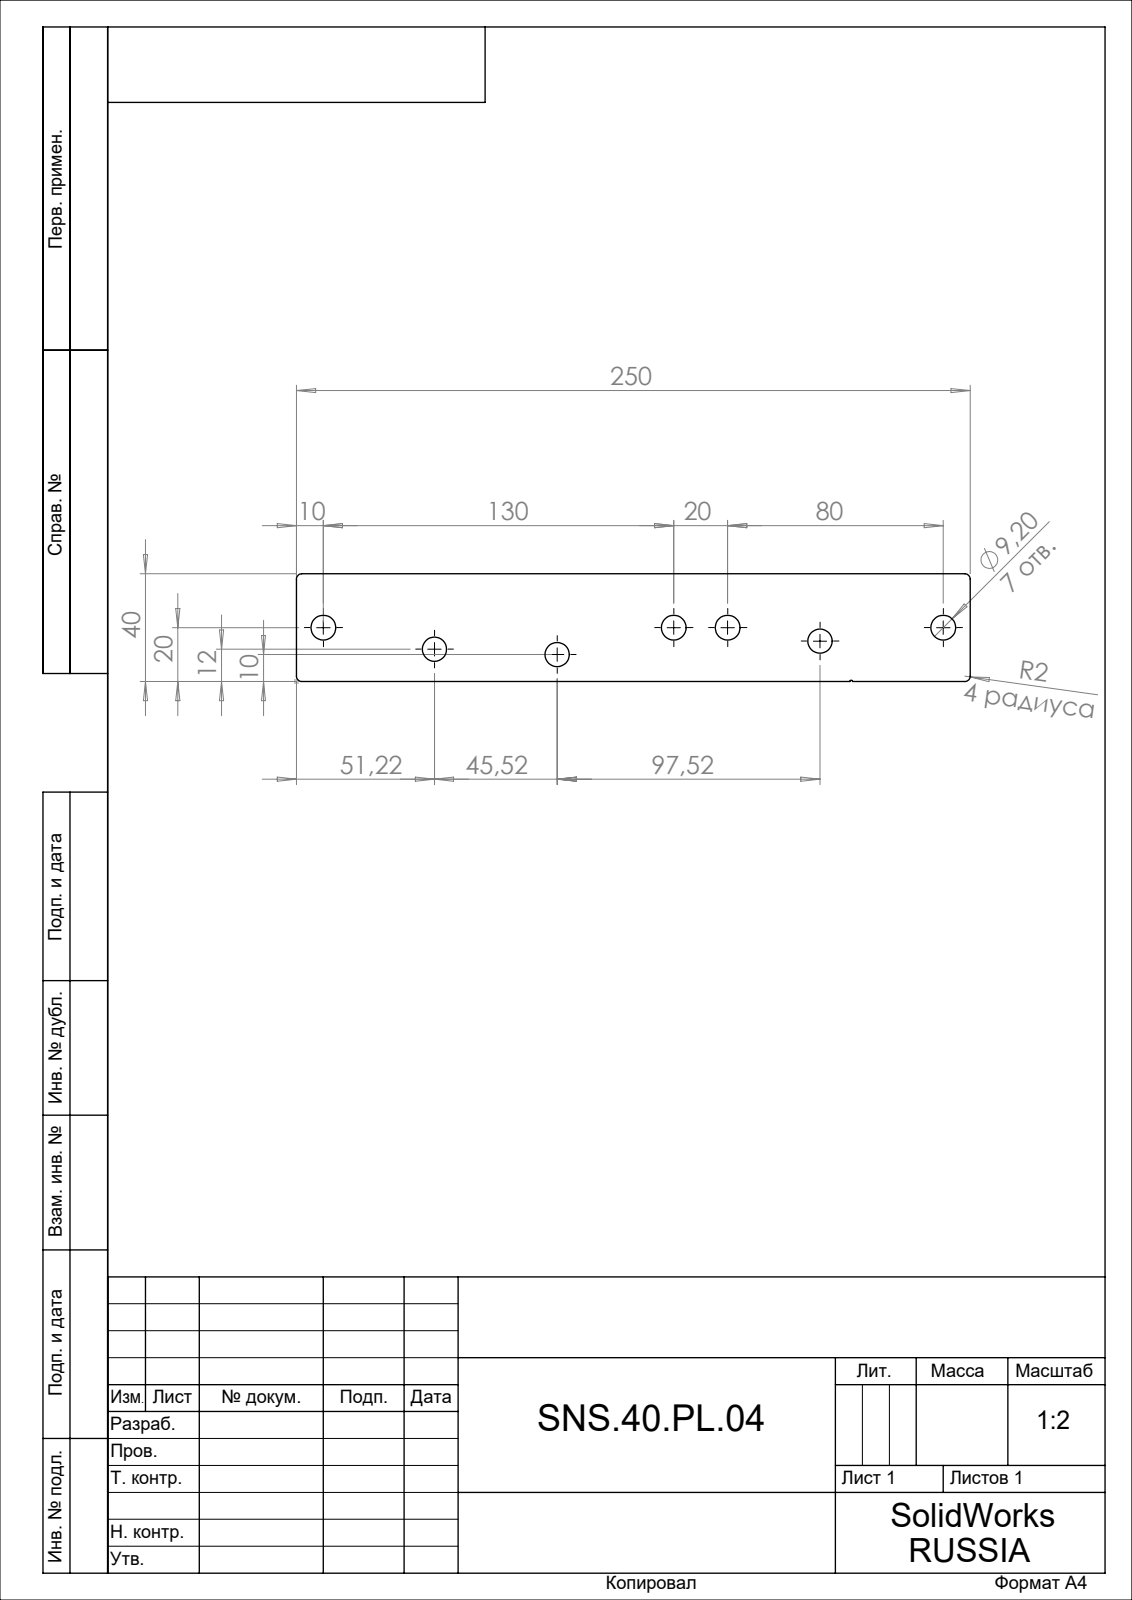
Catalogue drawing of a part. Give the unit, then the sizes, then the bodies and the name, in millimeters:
Units: millimetres
Overall size (bounding box): 250 × 40 × 5
Round holes (diameter × count): ⌀9.2 ×4, ⌀9 ×3
Partial cylindrical surfaces — rounded edges, fillets, slot ends (radius × count): R2 ×4, R0.5 ×1
Main face-to-face distances: 5, 40, 250
Hole centre spacings: 20, 34.62, 41.99, 44.4, 45.56, 46.01, 54.49, 64.05
Volume: 47 697 mm³ · Surface area: 22 967 mm²
Bodies: 1 solid, 26 faces (7 planar, 19 cylindrical, 0 other)
STEP written by: SolidWorks 2018 (AUTOMOTIVE_DESIGN)
